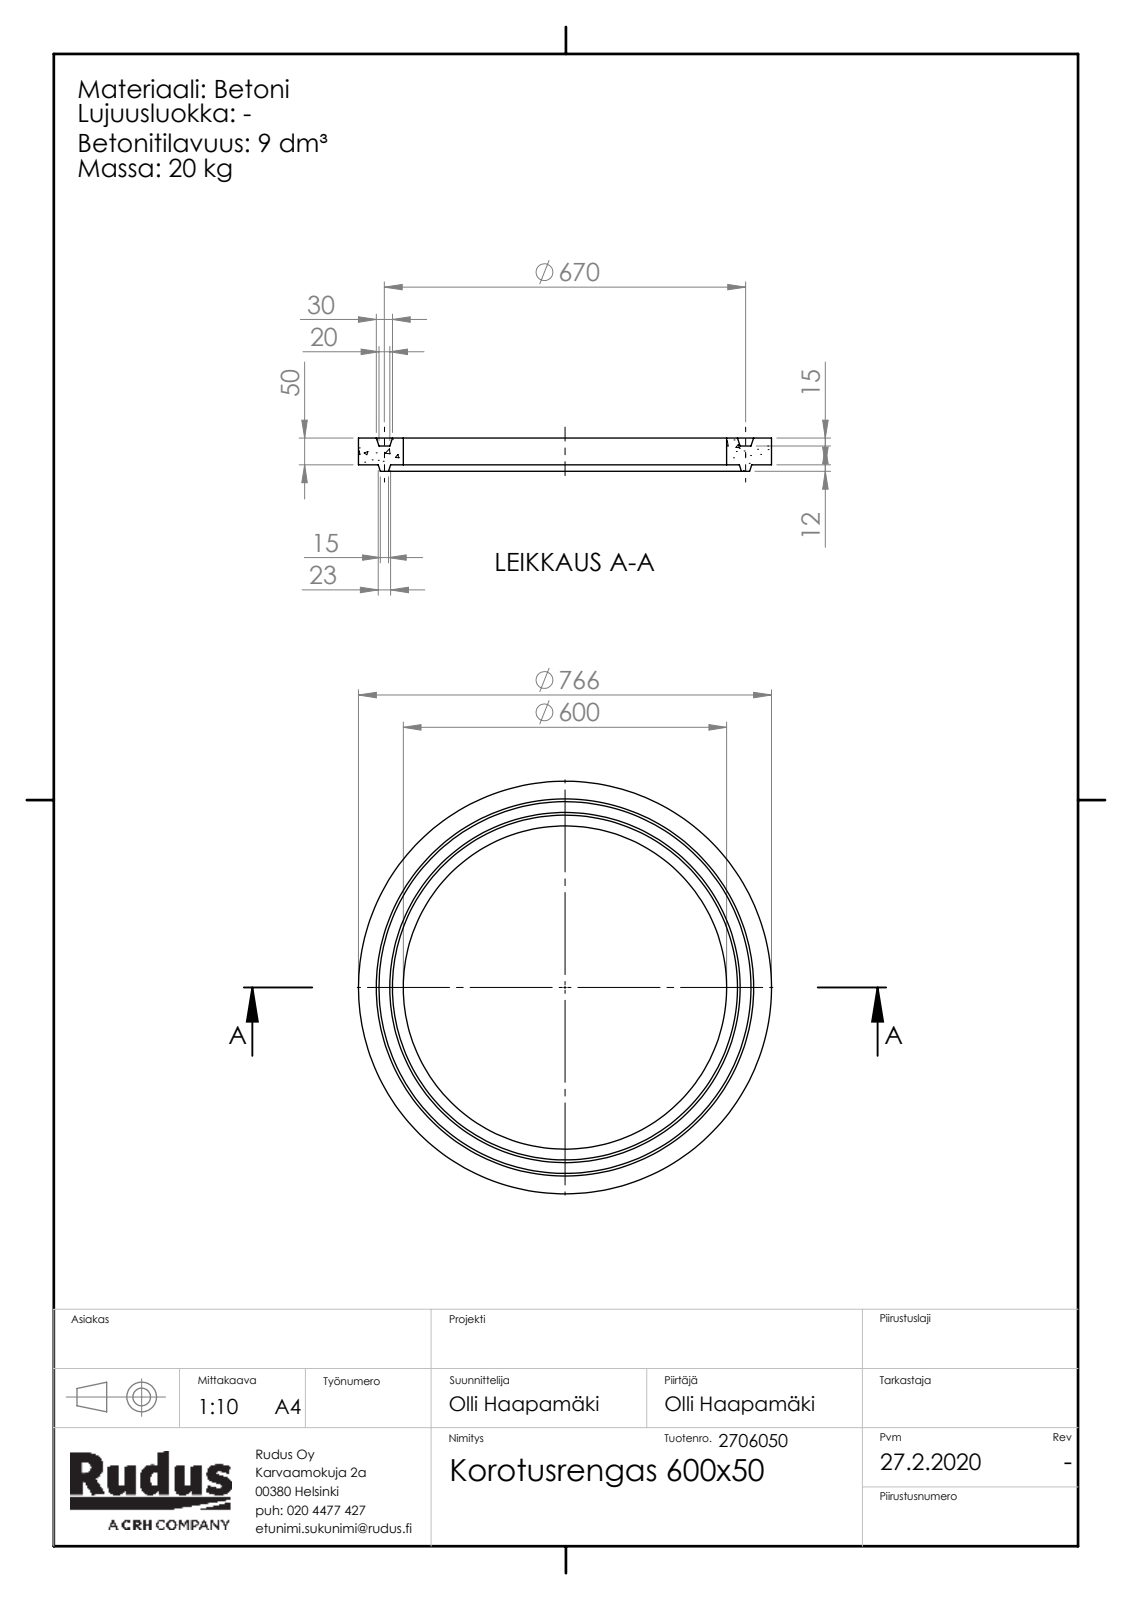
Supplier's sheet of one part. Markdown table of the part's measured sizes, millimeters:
| quantity | value |
| --- | --- |
| part name | Rudus 2706050 Korotusrengas 600x50; kaivo-osa-korotusrengas |
| STEP written by | SolidWorks 2019 (CONFIG_CONTROL_DESIGN) |
| units | millimeters |
| bodies | 1 solid, 18 faces (6 planar, 4 cylindrical, 8 other) |
| overall size | 766 × 766 × 62 |
| volume | 8 595 000 mm³ |
| surface area | 652 682 mm² |
| round holes (diameter × count) | 600 × 1 |
| round bosses / shafts (diameter × count) | 766 × 1 |
| main face-to-face distances | 50, 15, 35, 62, 47, 12 |
